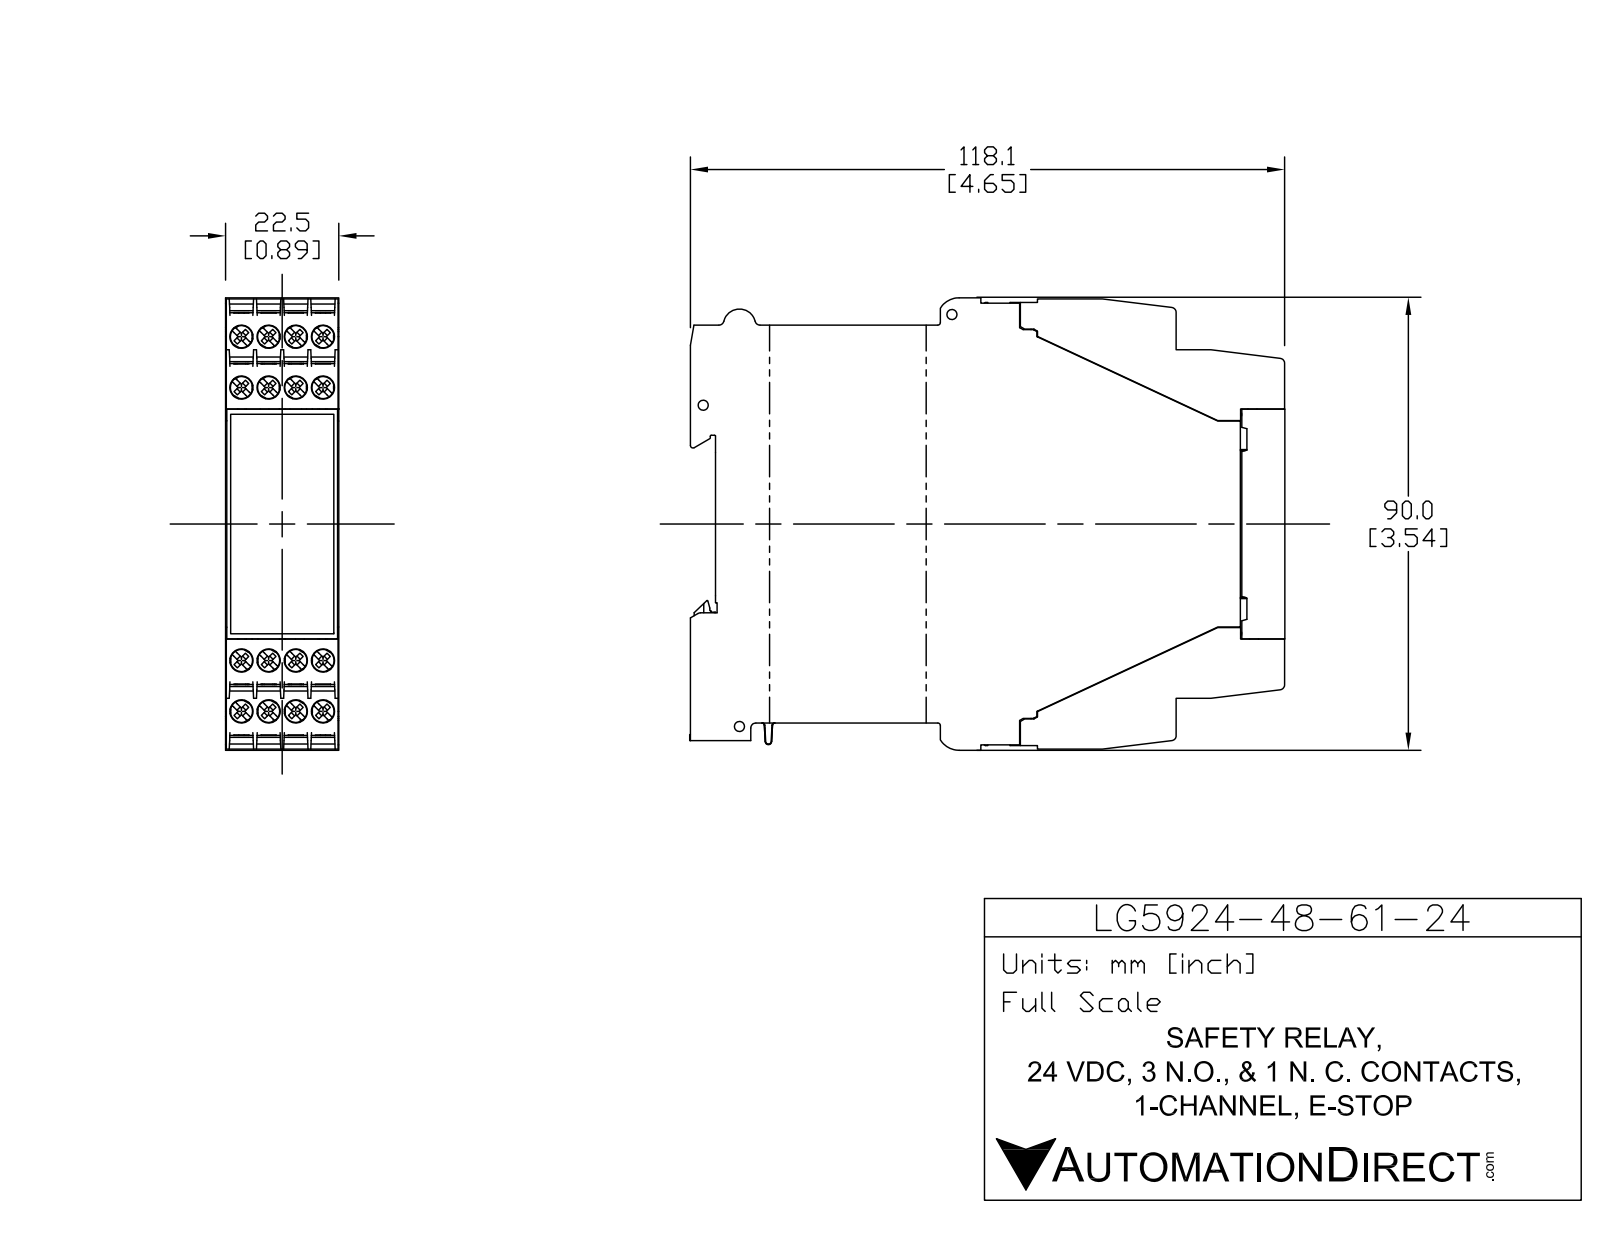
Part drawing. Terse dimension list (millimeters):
name: LG5924-02-61-24
written by: SolidWorks 2017 (AUTOMOTIVE_DESIGN)
unit: mm
bodies: 18 solids, 940 faces (815 planar, 83 cylindrical, 42 other)
size: 118 × 101.9 × 23
volume: 238 600 mm³; area: 47 570 mm²
holes: 4× ⌀1, 4× ⌀1.7, 1× ⌀1.2
bosses: 1× ⌀1.3
rounds: 10× R0.1, 8× R1, 7× R0.5, 6× R0.1, 4× R0.1, 3× R0.2, 3× R0.5, 2× R0.3
face distances: 23, 22.8, 10.1, 22.9, 22.6, 59.6, 4.6, 74.3, 21.5, 14.8
hole spacings: 16.2, 21.5, 26.9
